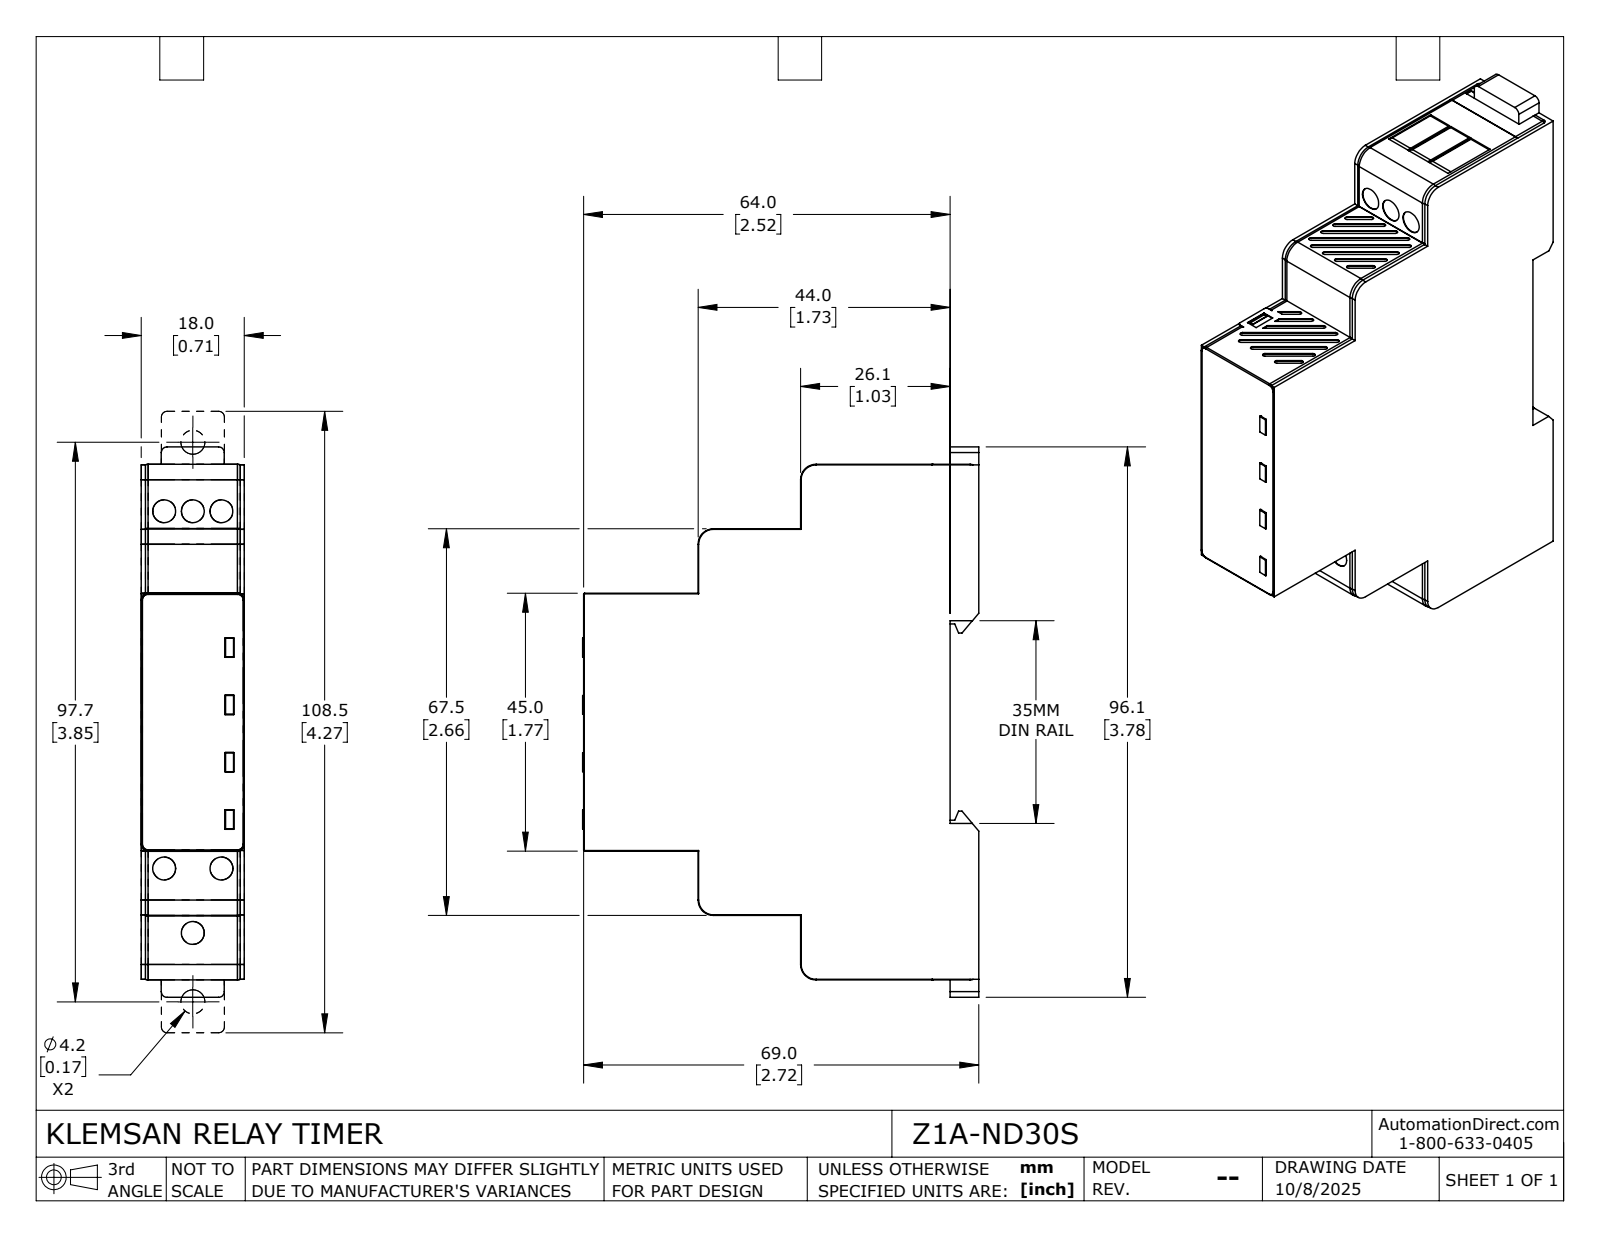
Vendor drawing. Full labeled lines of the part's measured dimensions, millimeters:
Part name (STEP PRODUCT): Z1A-ND30S
STEP written by: SolidWorks 2024 (CONFIG_CONTROL_DESIGN)
Units: millimetres
Bodies: 3 solids, 440 faces (280 planar, 60 cylindrical, 100 other)
Overall size (bounding box): 96.07 × 69.15 × 18
Volume: 83 847 mm³ · Surface area: 17 884 mm²
Round holes (diameter × count): ⌀4.2 ×2, ⌀4 ×1
Partial cylindrical surfaces — rounded edges, fillets, slot ends (radius × count): R1.2 ×16, R0.2 ×4, R1 ×4, R2.6 ×4, R2.7 ×4, R0.5 ×2, R1.5 ×2
Main face-to-face distances: 18, 3.5, 14.5, 11.25, 64, 5, 69, 22.5, 67.4, 67.5
Hole centre spacings: 5.83, 79.43, 85.26
